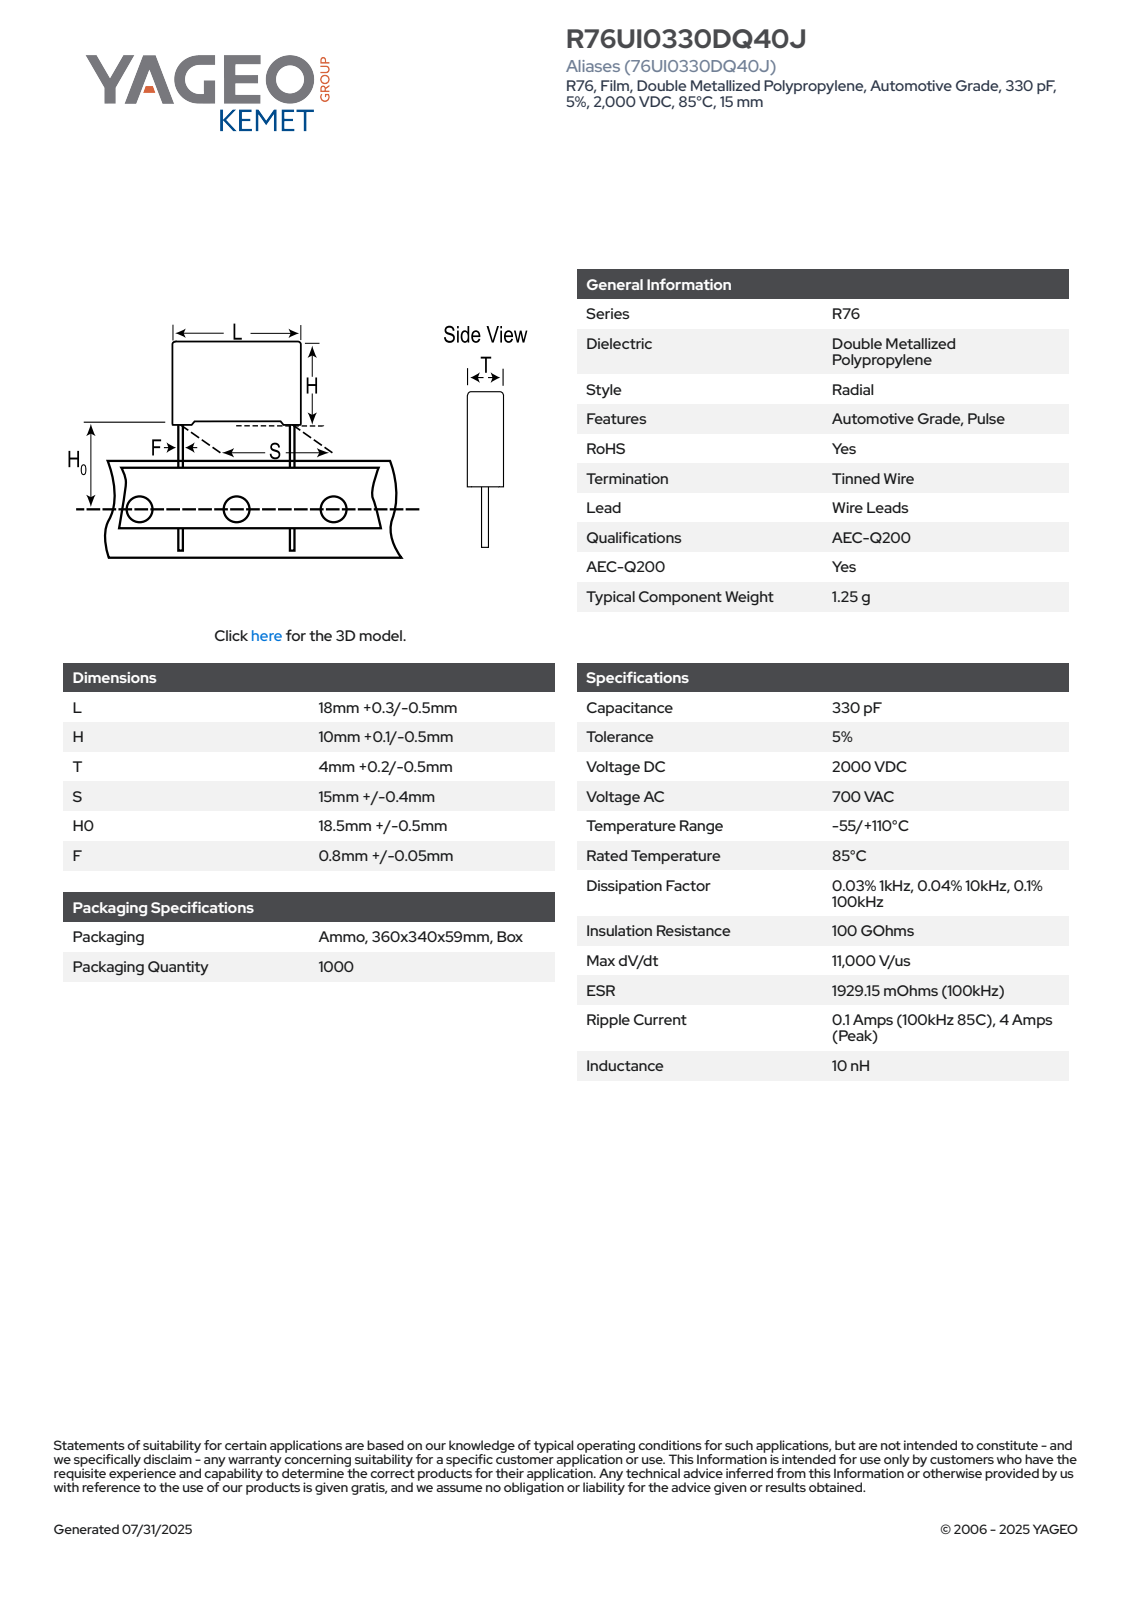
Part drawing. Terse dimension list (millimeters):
name: CFR_RB2_18X10X4_L18.3H10.1T4.2S15H019F0.85
written by: SolidWorks 2020 (AUTOMOTIVE_DESIGN)
unit: mm
bodies: 4 solids, 85 faces (77 planar, 8 cylindrical, 0 other)
size: 29.1 × 18.3 × 4.21
volume: 753 mm³; area: 743 mm²
bosses: 2× ⌀0.85
rounds: 4× R0.5
face distances: 4.2, 9.35, 18.3, 0.61, 3.59, 0.4, 9.75, 0.75, 0.35, 10.1
